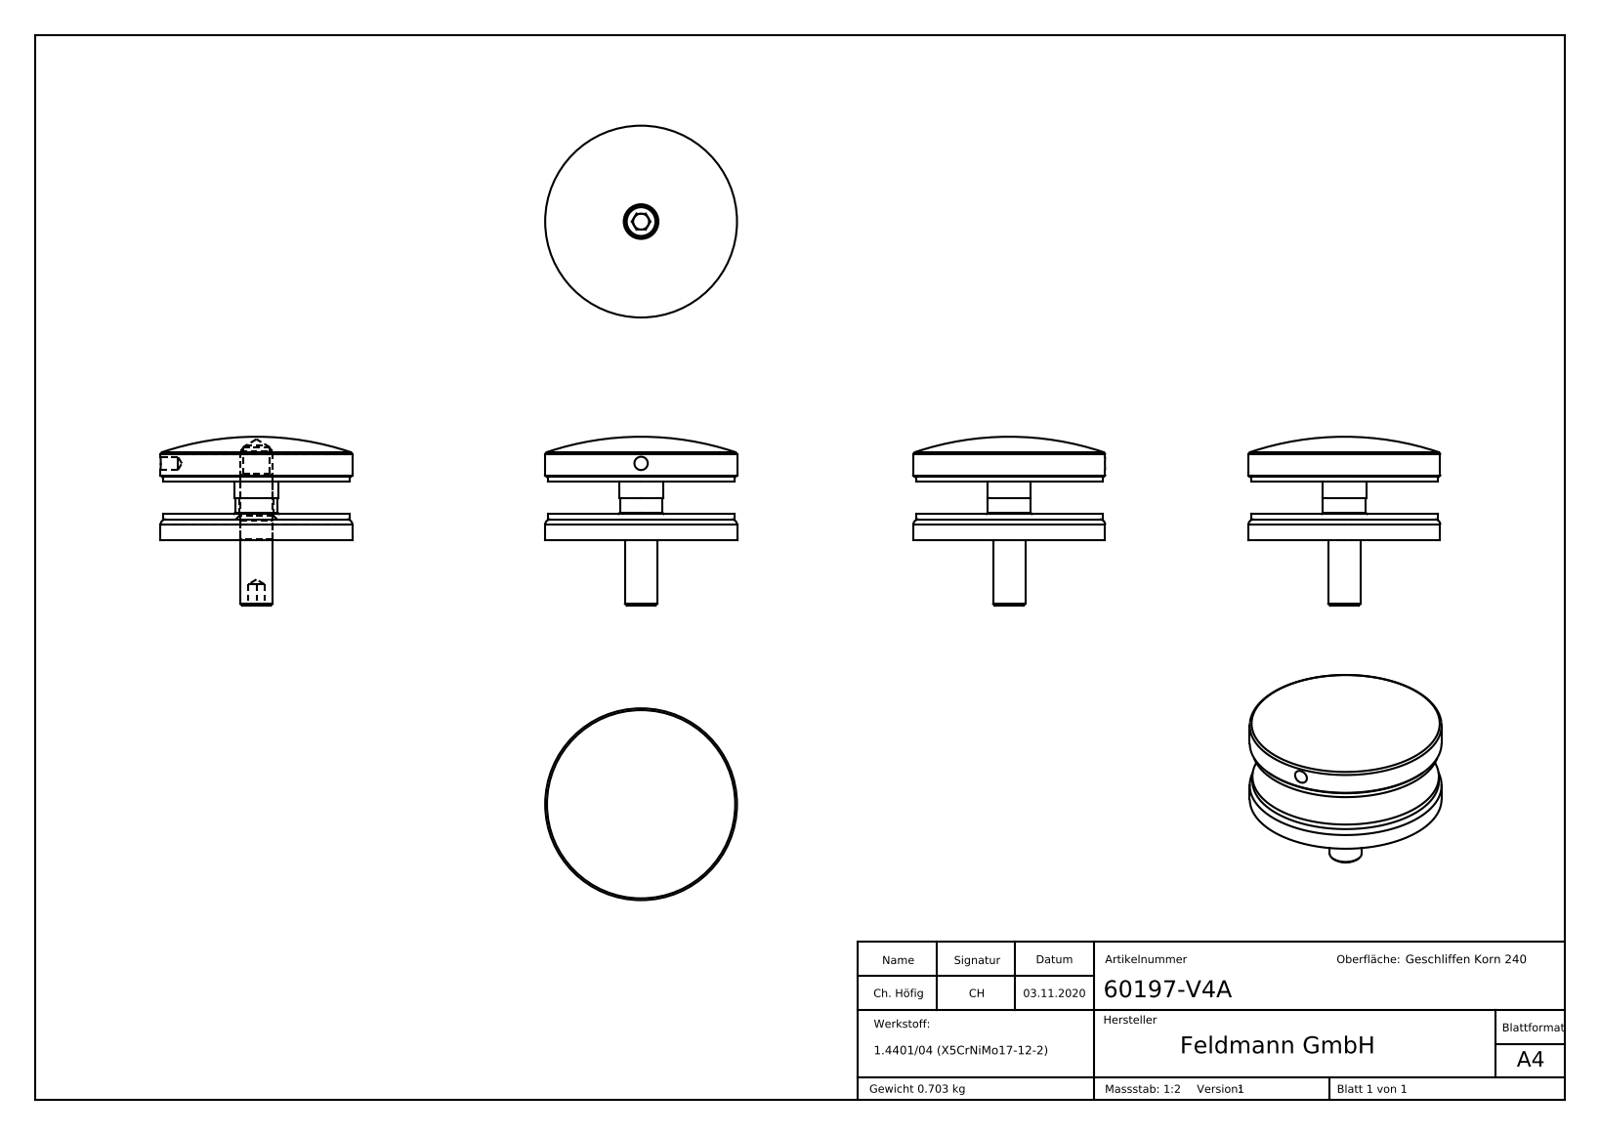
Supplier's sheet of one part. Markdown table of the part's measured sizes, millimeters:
| quantity | value |
| --- | --- |
| part name | DIN913; 60197-XXX Teil2_60197-V4A Teil2; 60197-XXX Teil5_60197-XXX Teil5; 60197-XXX Teil5 (+8 more) |
| STEP written by | SolidWorks 2018 (CONFIG_CONTROL_DESIGN) |
| units | millimeters |
| bodies | 6 solids, 285 faces (156 planar, 26 cylindrical, 103 other) |
| overall size | 72 × 72 × 65.38 |
| volume | 101 625 mm³ |
| surface area | 40 221 mm² |
| round holes (diameter × count) | 5 × 1, 10.2 × 1, 12 × 1, 12.5 × 1 |
| round bosses / shafts (diameter × count) | 72 × 1, 70 × 1, 16.3 × 1, 16 × 1 |
| main face-to-face distances | 2, 14, 16, 8, 24, 22, 10, 12, 6, 24.38 |
